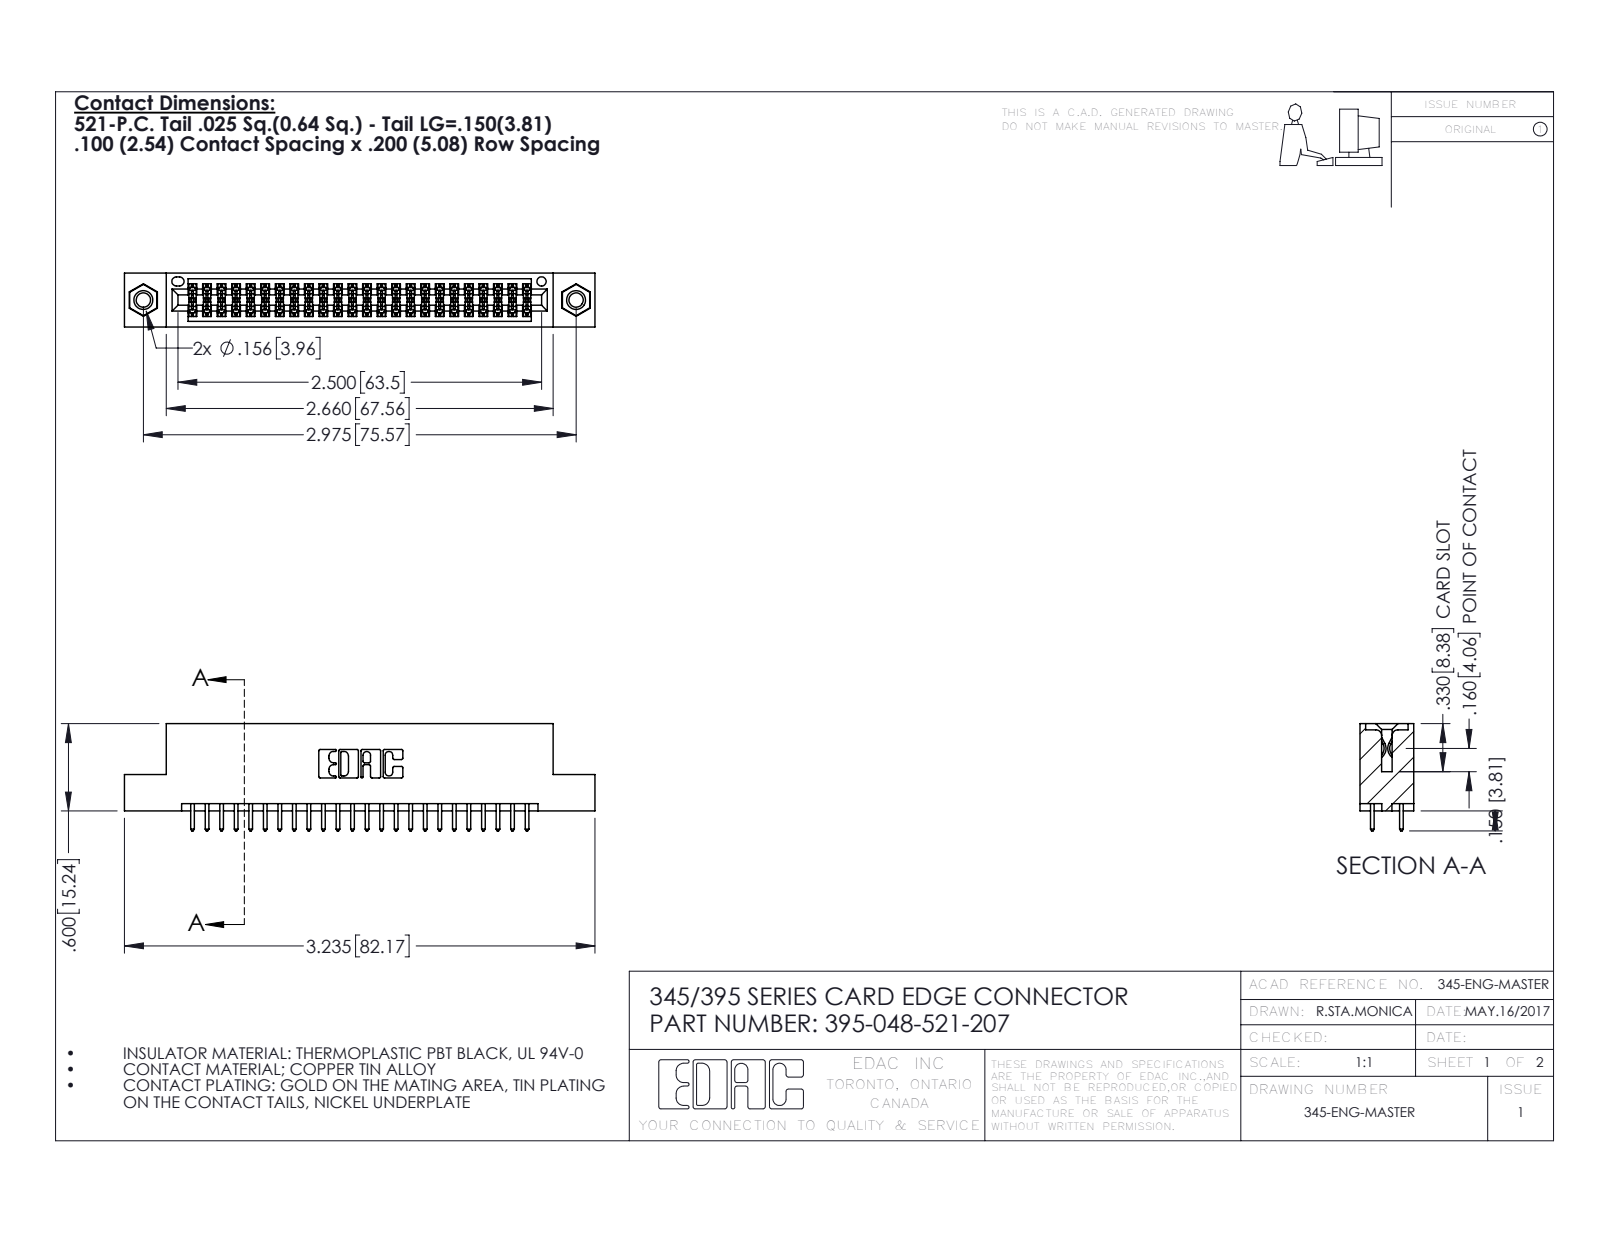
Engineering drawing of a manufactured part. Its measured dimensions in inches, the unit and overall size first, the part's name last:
Units: inches
Overall size (bounding box): 3.235 × 0.737 × 0.37
Round holes (diameter × count): ⌀0.098 ×2, ⌀0.125 ×2, ⌀0.156 ×2, ⌀0.064 ×1
Round bosses / shafts (diameter × count): ⌀0.155 ×2
Partial cylindrical surfaces — rounded edges, fillets, slot ends (radius × count): R0.006 ×72, R0.01 ×48, R0.01 ×22, R0.007 ×6, R0.031 ×6, R0.026 ×3, R0.014 ×2, R0.019 ×2
Main face-to-face distances: 0.072, 0.298, 0.2, 0.37, 0.098, 0.272, 0.025, 0.225, 0.175, 0.149
Hole centre spacings: 0.27, 2.741, 2.975
Volume: 0.475 in³ · Surface area: 17.13 in²
Bodies: 51 solids, 2586 faces (1696 planar, 874 cylindrical, 16 other)
Part name (STEP PRODUCT): 345 Part_Flush Mounting Lugs - 0.156 Dia-TI; 395-048-521-207; 345-292-001_345-293-121; 345-250-001_345-250-005-103
STEP written by: SolidWorks 2016 (CONFIG_CONTROL_DESIGN)
